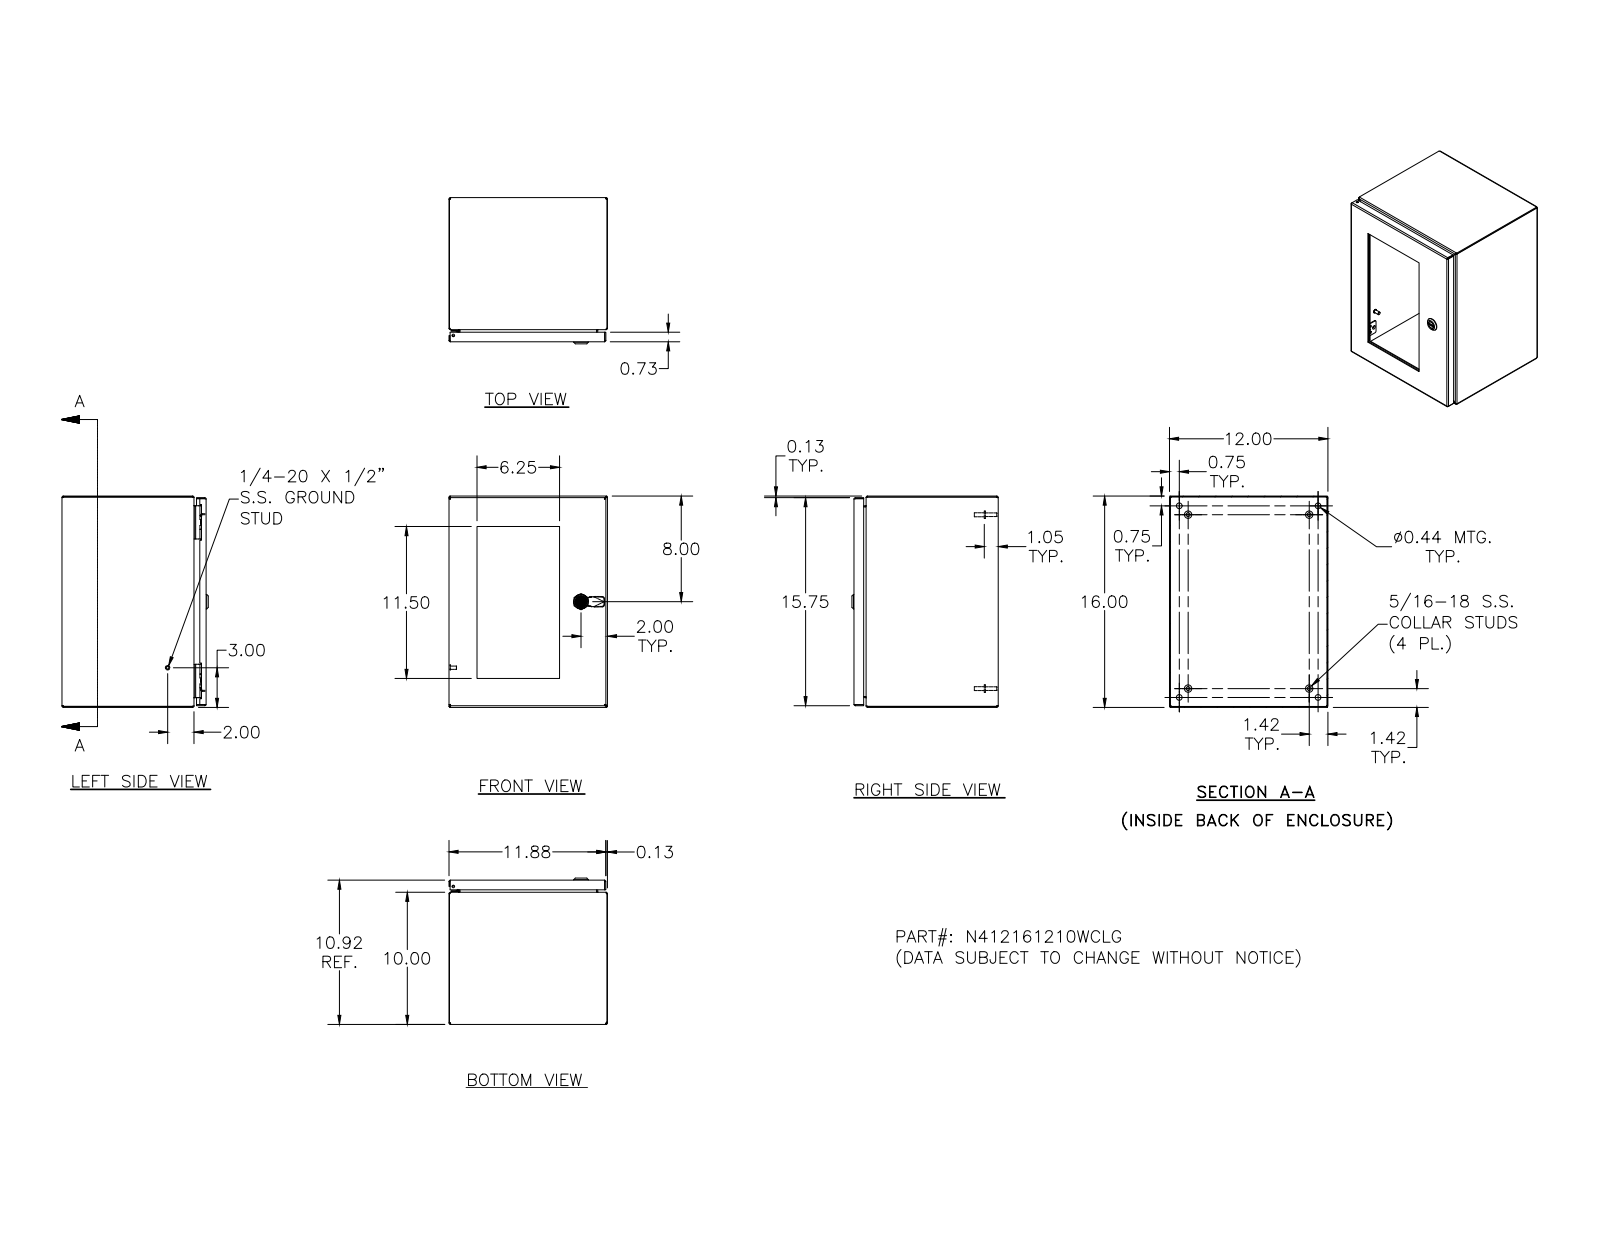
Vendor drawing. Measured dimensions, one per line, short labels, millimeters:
name: N412161210WCLG
written by: SolidWorks 2018 (AUTOMOTIVE_DESIGN)
unit: mm
bodies: 57 solids, 1827 faces (687 planar, 593 cylindrical, 547 other)
size: 406.4 × 304.8 × 281.3
volume: 1 629 000 mm³; area: 1 479 000 mm²
holes: 12× ⌀4, 10× ⌀7.1, 5× ⌀4.8, 4× ⌀2.4, 4× ⌀3.9, 4× ⌀4.2, 4× ⌀4.4, 4× ⌀11.1, 1× ⌀4.7, 1× ⌀5, 1× ⌀8, 1× ⌀10
bosses: 10× ⌀8.6, 10× ⌀6.4, 10× ⌀4.8, 4× ⌀14.3, 4× ⌀9.1, 4× ⌀8.1, 4× ⌀7.6, 4× ⌀7
rounds: 34× R0.8, 30× R0.3, 26× R1.3, 24× R2.7, 18× R0.4, 16× R3.2, 13× R0.5, 8× R0.8
face distances: 1.9, 302.9, 275.4, 404.5, 273.5, 304.8, 301, 402.6, 406.4, 277.3
hole spacings: 101.6, 304.8, 158, 215.9, 218.1, 301.3, 190.5, 12.7
